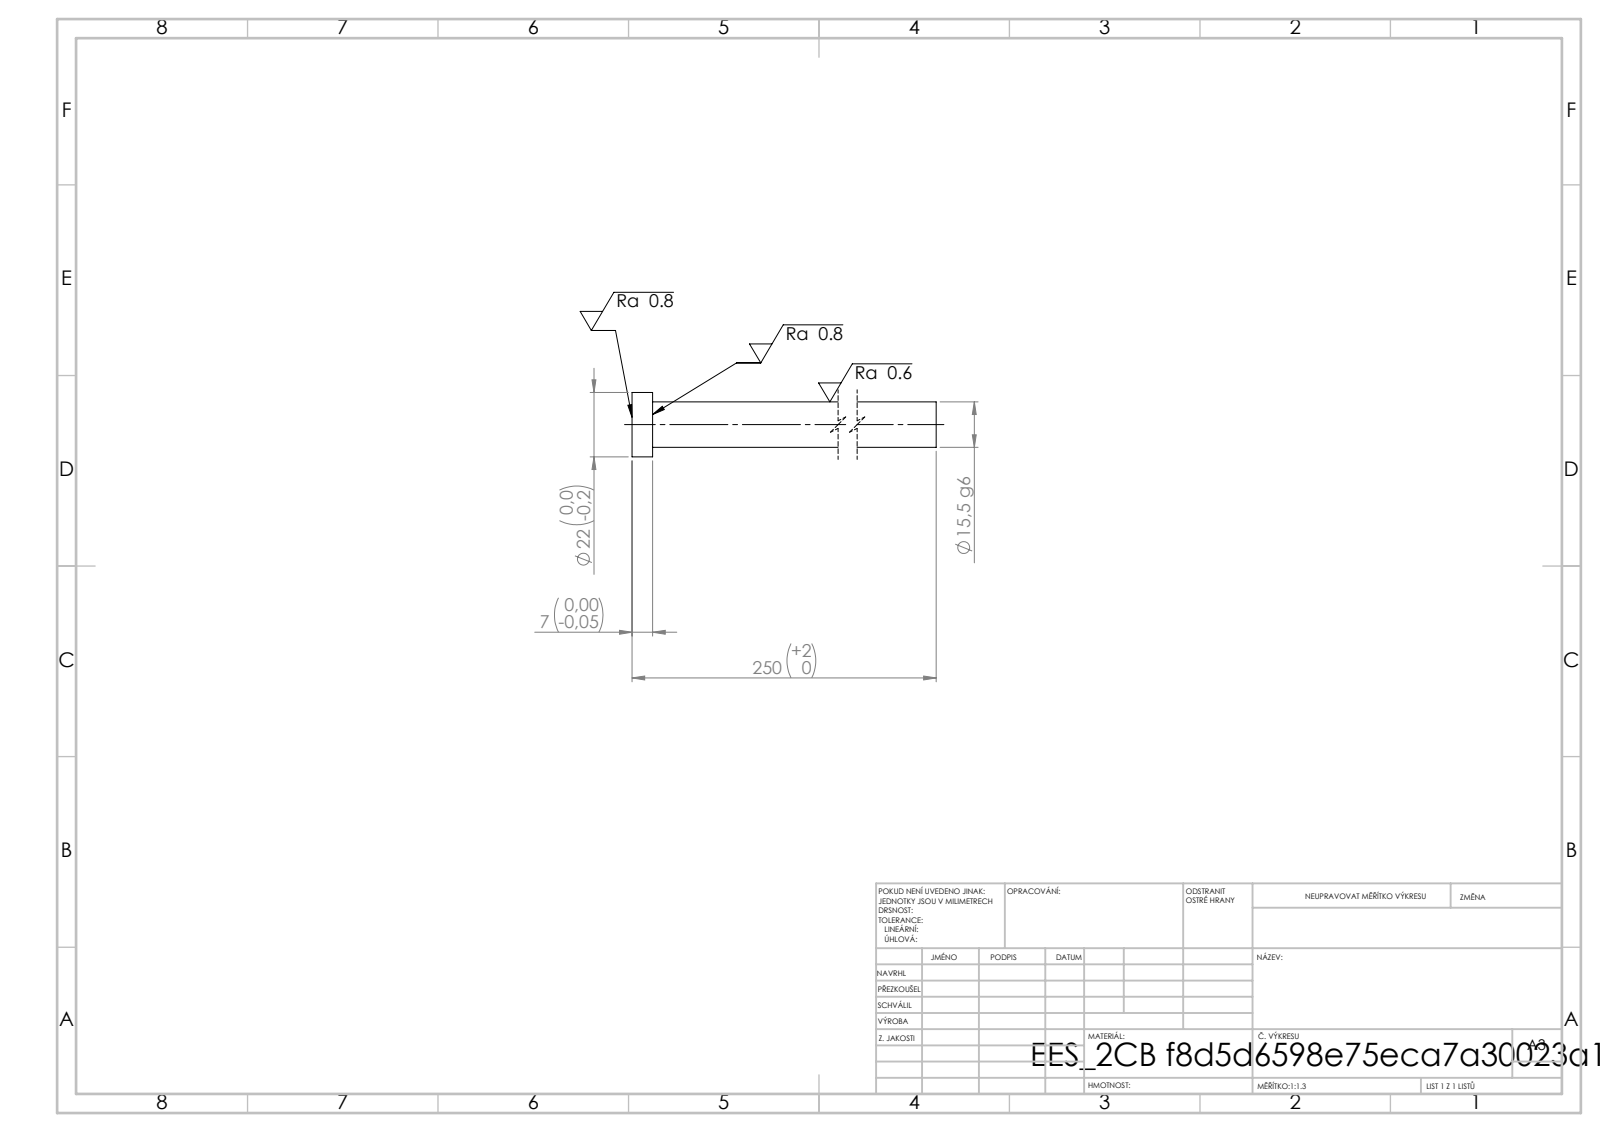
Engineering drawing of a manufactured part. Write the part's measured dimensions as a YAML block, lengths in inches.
step_written_by: "SolidWorks 2019 (CONFIG_CONTROL_DESIGN)"
units: inches
bodies: {solids: 1, faces: 7, planar: 3, cylindrical: 4, other: 0}
overall_size: [9.843, 0.866, 0.866]
volume: 2.96
surface_area: 20.27
round_bosses_or_shafts:
  - {diameter: 0.866, count: 1}
  - {diameter: 0.61, count: 1}
face_to_face_distances: [0.276, 9.843, 9.567]
